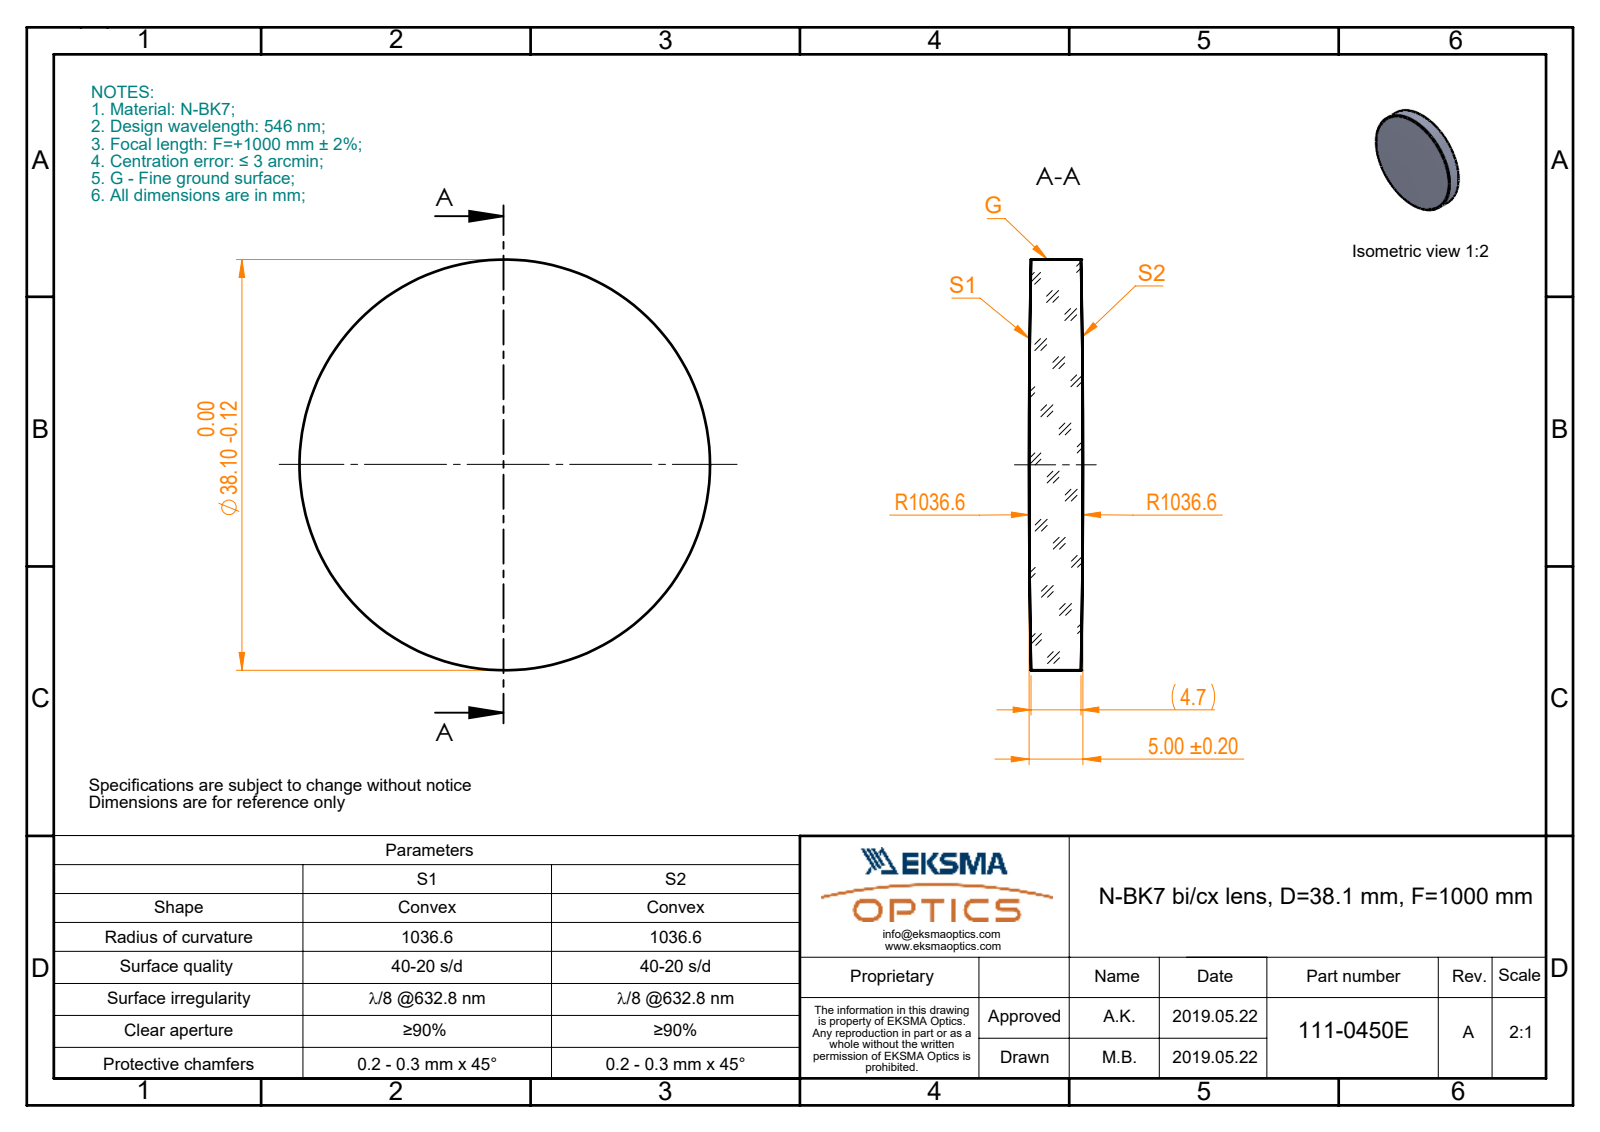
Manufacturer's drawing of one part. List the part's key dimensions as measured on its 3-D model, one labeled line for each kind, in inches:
Part name (STEP PRODUCT): 111-0450E BK7 bi-cx 38.1 F1000
STEP written by: SolidWorks 2017 (CONFIG_CONTROL_DESIGN)
Units: inches
Bodies: 1 solid, 6 faces (0 planar, 2 cylindrical, 4 other)
Overall size (bounding box): 1.5 × 1.5 × 0.197
Volume: 0.336 in³ · Surface area: 4.397 in²
Round bosses / shafts (diameter × count): ⌀1.5 ×1
